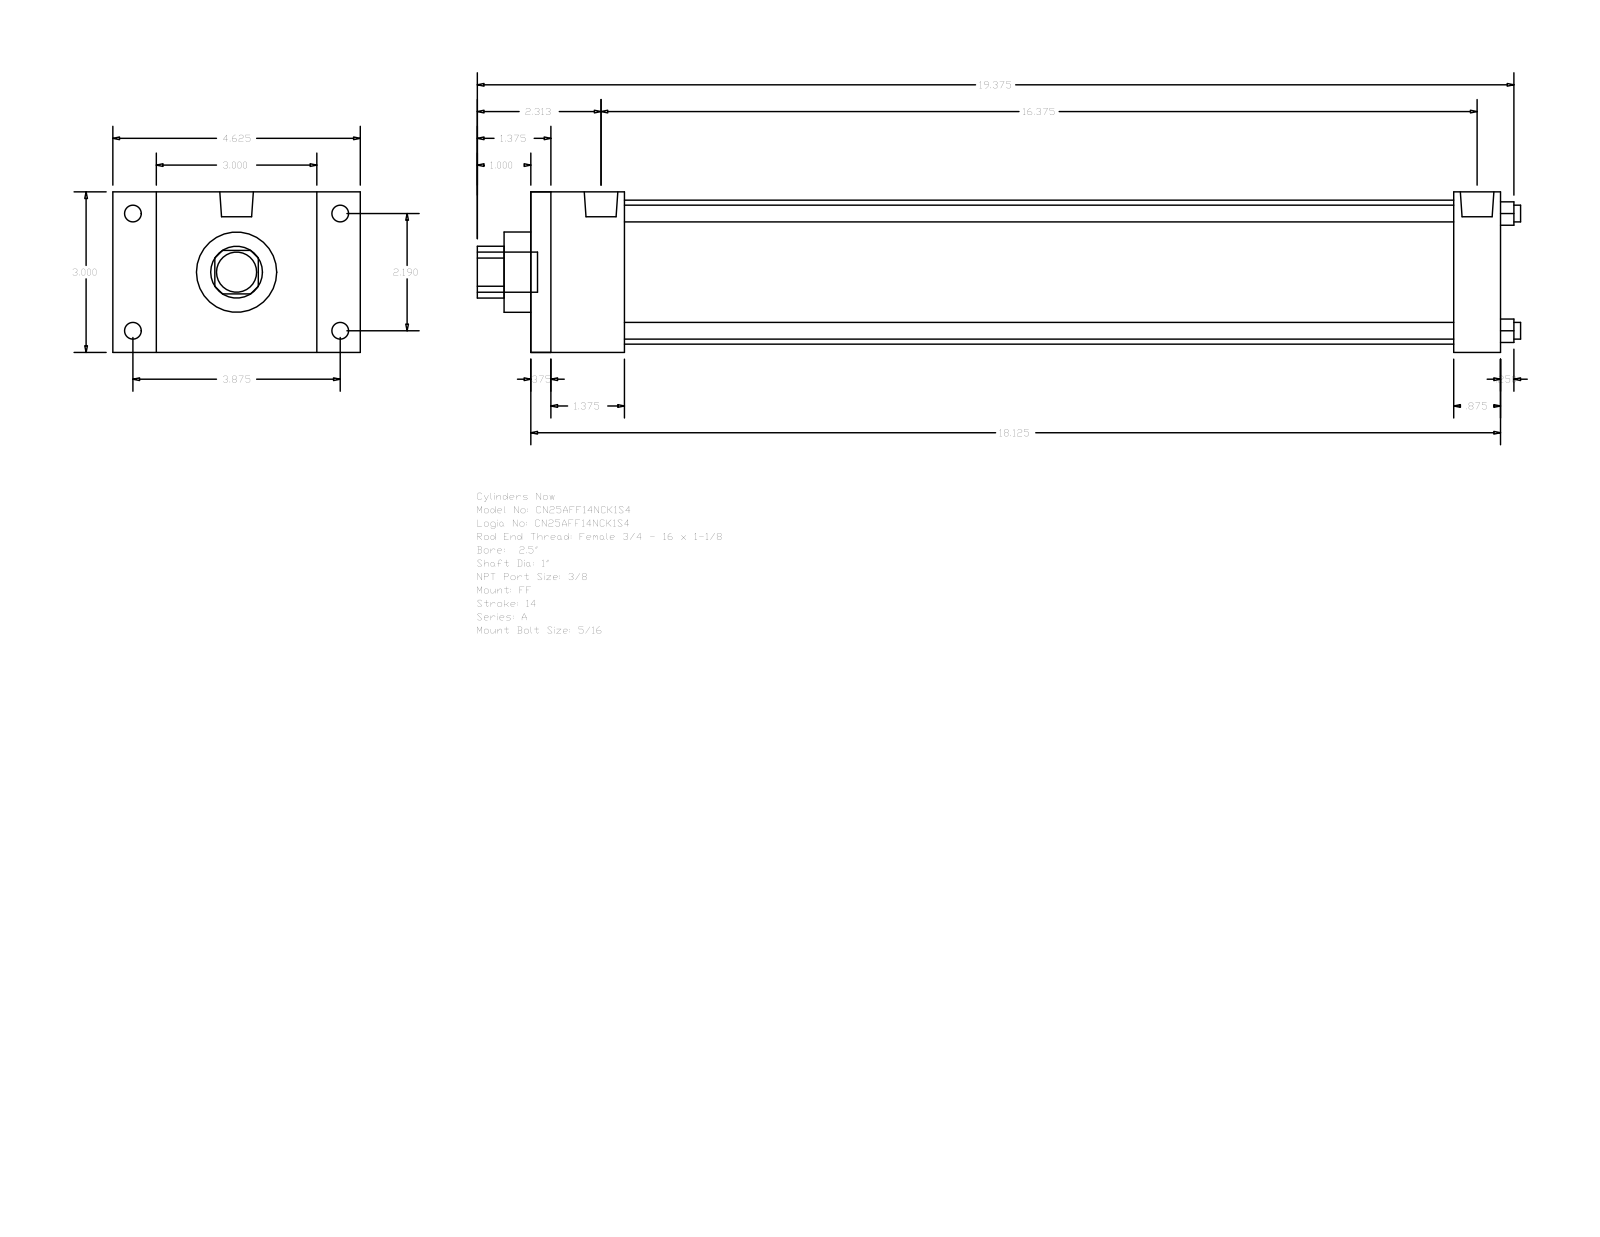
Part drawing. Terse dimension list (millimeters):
name: A_FF__0250_1
written by: GSSL Pune (CONFIG_CONTROL_DESIGN)
unit: mm
bodies: 0 solids, 92 faces (64 planar, 28 cylindrical, 0 other)
size: 495.3 × 117.47 × 76.2
holes: 4× ⌀7.94, 1× ⌀25.4, 1× ⌀38.1, 1× ⌀68.33
bosses: 4× ⌀7.94, 4× ⌀5.56, 2× ⌀15.93, 1× ⌀19.05
rounds: 1× R12.29
face distances: 76.2, 460.37, 450.85, 9.52, 22.22, 44.45, 438.15, 34.93, 428.63, 393.7
hole spacings: 39.33, 55.62, 78.66
